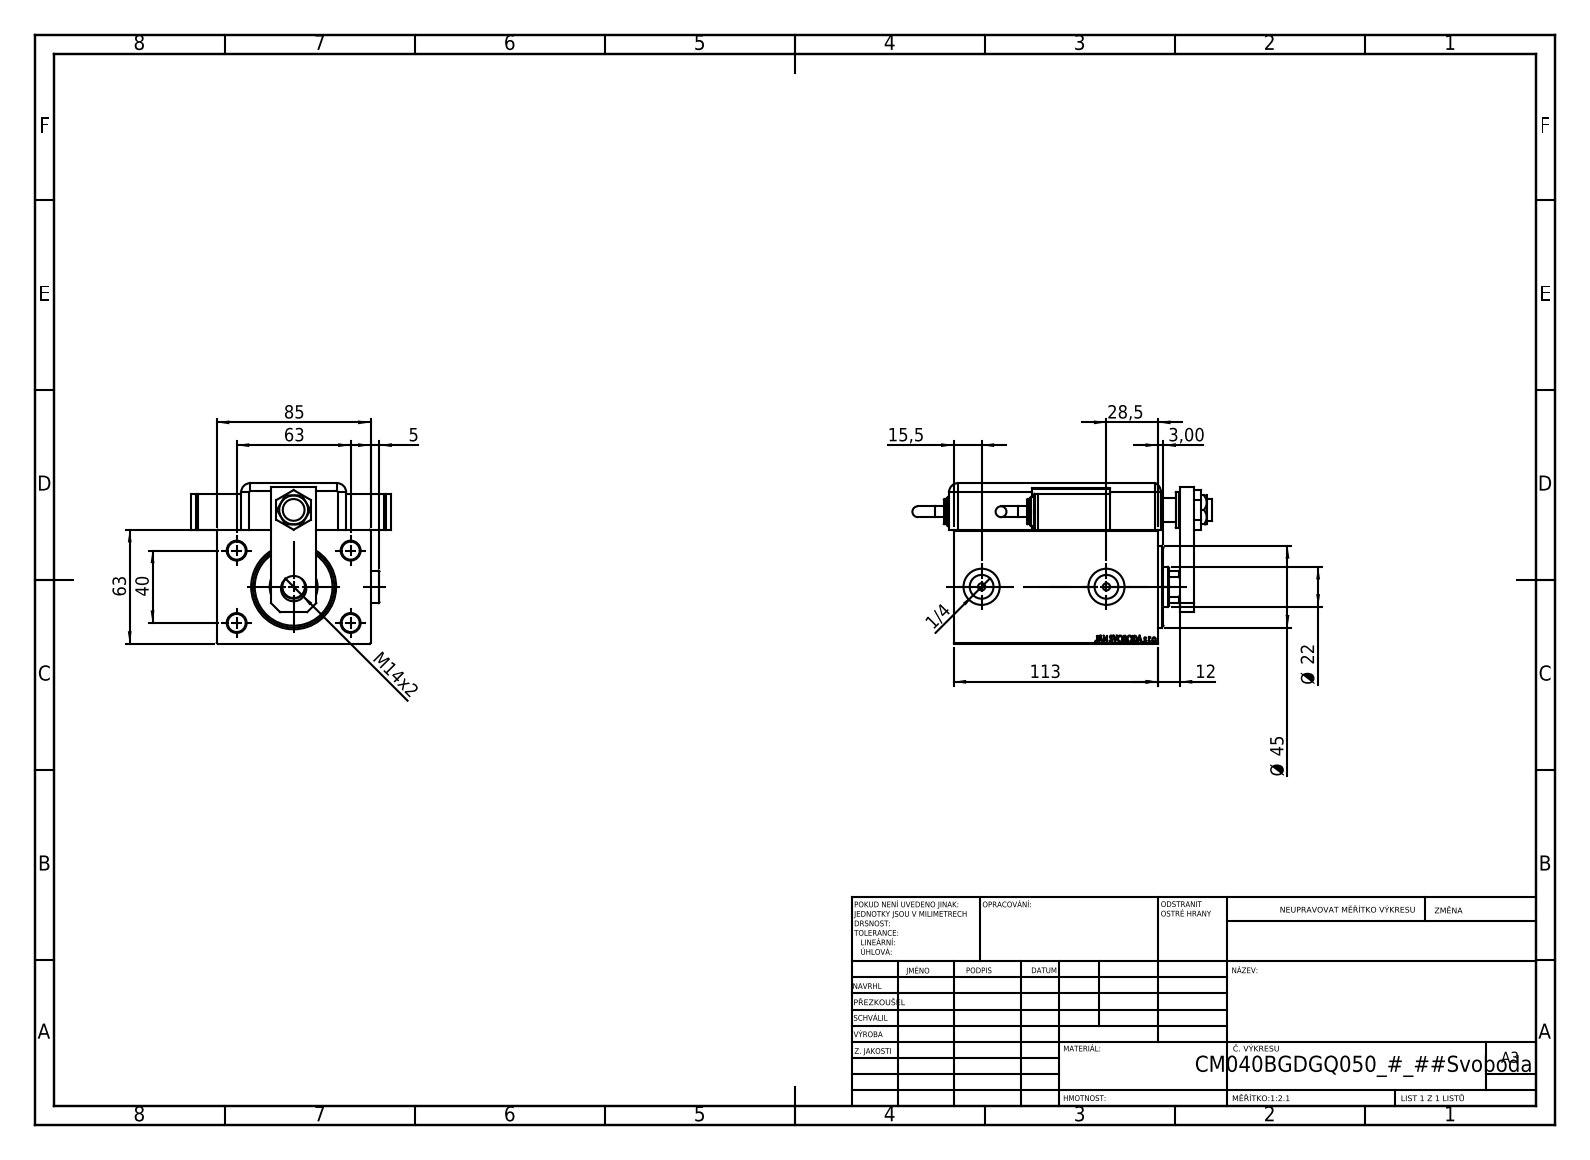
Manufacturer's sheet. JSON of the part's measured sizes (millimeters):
{"part_name": "MAGNETIC SWITCH Q; KRYT; NUT_D13; V450CM_VC_B (+7 more)", "step_written_by": "SolidWorks 2019 (CONFIG_CONTROL_DESIGN)", "units": "millimeters", "bodies": {"solids": 15, "faces": 1319, "planar": 641, "cylindrical": 125, "other": 553}, "overall_size": [165.46, 111, 88.8], "volume_mm3": 692815, "surface_area_mm2": 141667, "round_holes": [[4, 4], [10, 4], [8, 2], [13.16, 2], [14, 2], [20, 2], [12, 1], [12.5, 1], [13, 1], [22, 1], [25.5, 1], [26.5, 1]], "round_bosses_or_shafts": [[20, 3], [18, 2], [16, 2], [14, 2], [6, 2]], "partial_cylinders_radius": [[5, 9], [10, 1], [10.5, 1]], "face_to_face_distances": [3, 63, 85, 13.5, 12, 25.8, 88.8, 113, 20, 83], "hole_center_spacings": [37.31, 36.79, 37.86, 38.71, 40, 63, 69.99, 74.63]}
